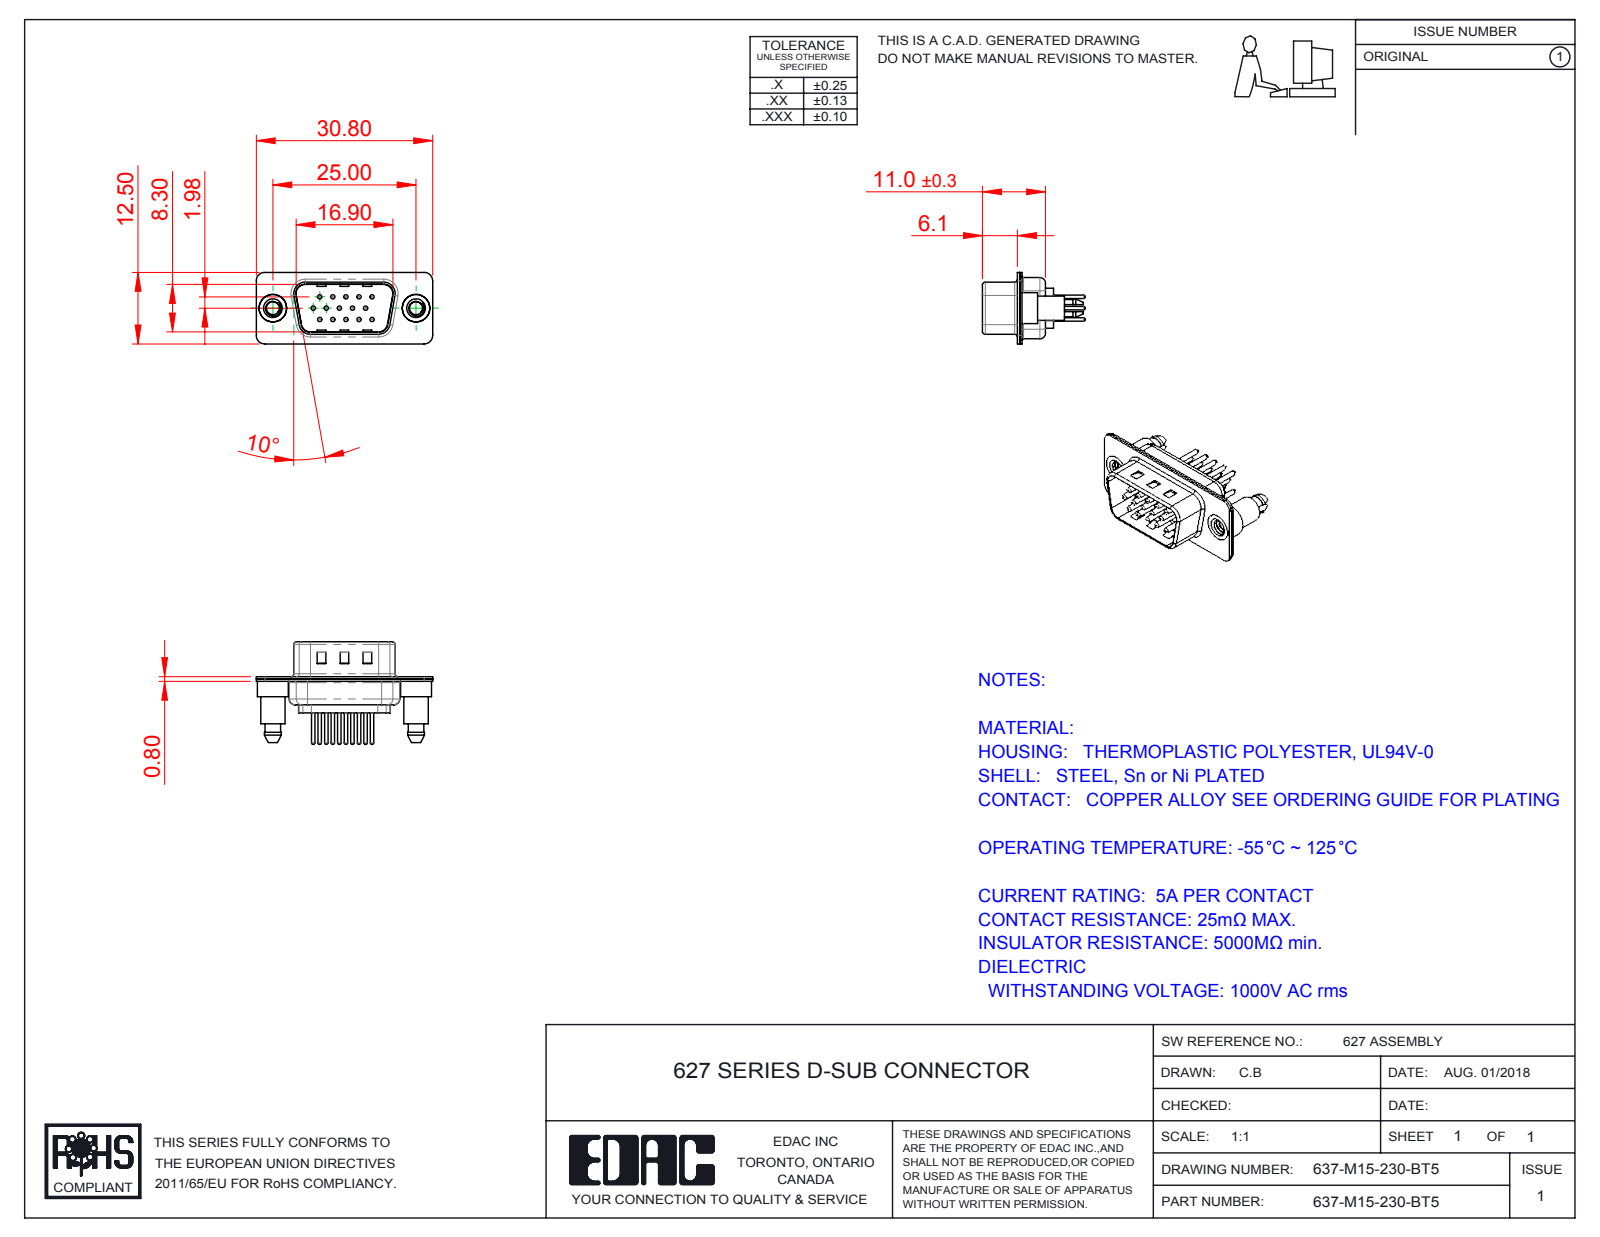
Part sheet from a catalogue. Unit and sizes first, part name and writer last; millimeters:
Units: millimetres
Overall size (bounding box): 30.8 × 17.9 × 12.5
Round holes (diameter × count): ⌀0.75 ×15, ⌀1.6 ×15, ⌀2 ×15, ⌀2.26 ×2, ⌀4 ×2, ⌀4.8 ×2
Round bosses / shafts (diameter × count): ⌀1.5 ×15, ⌀0.6 ×15, ⌀5.4 ×2, ⌀4.9 ×2, ⌀4.25 ×2
Partial cylindrical surfaces — rounded edges, fillets, slot ends (radius × count): R1.5 ×18, R2 ×12, R1.6 ×10, R0.5 ×8, R0.25 ×4, R0.6 ×4, R0.65 ×4, R0.9 ×4
Main face-to-face distances: 0.4, 0.8, 9.5, 9.1, 0.65, 8.7, 9.9, 6.3, 1.4, 0.75
Hole centre spacings: 3.96, 2.28, 2.29, 4.57, 6.05, 6.86, 7.92, 6.04
Volume: 1 483 mm³ · Surface area: 4 425 mm²
Bodies: 20 solids, 909 faces (228 planar, 371 cylindrical, 310 other)
Part name (STEP PRODUCT): 637M 4-40 Threaded Boardlock; 637M Contact Row 2_30; 637M Contact Row 1_30; 637M Shell Rear_15 Contacts (+4 more)
STEP written by: SolidWorks 2016 (CONFIG_CONTROL_DESIGN)
